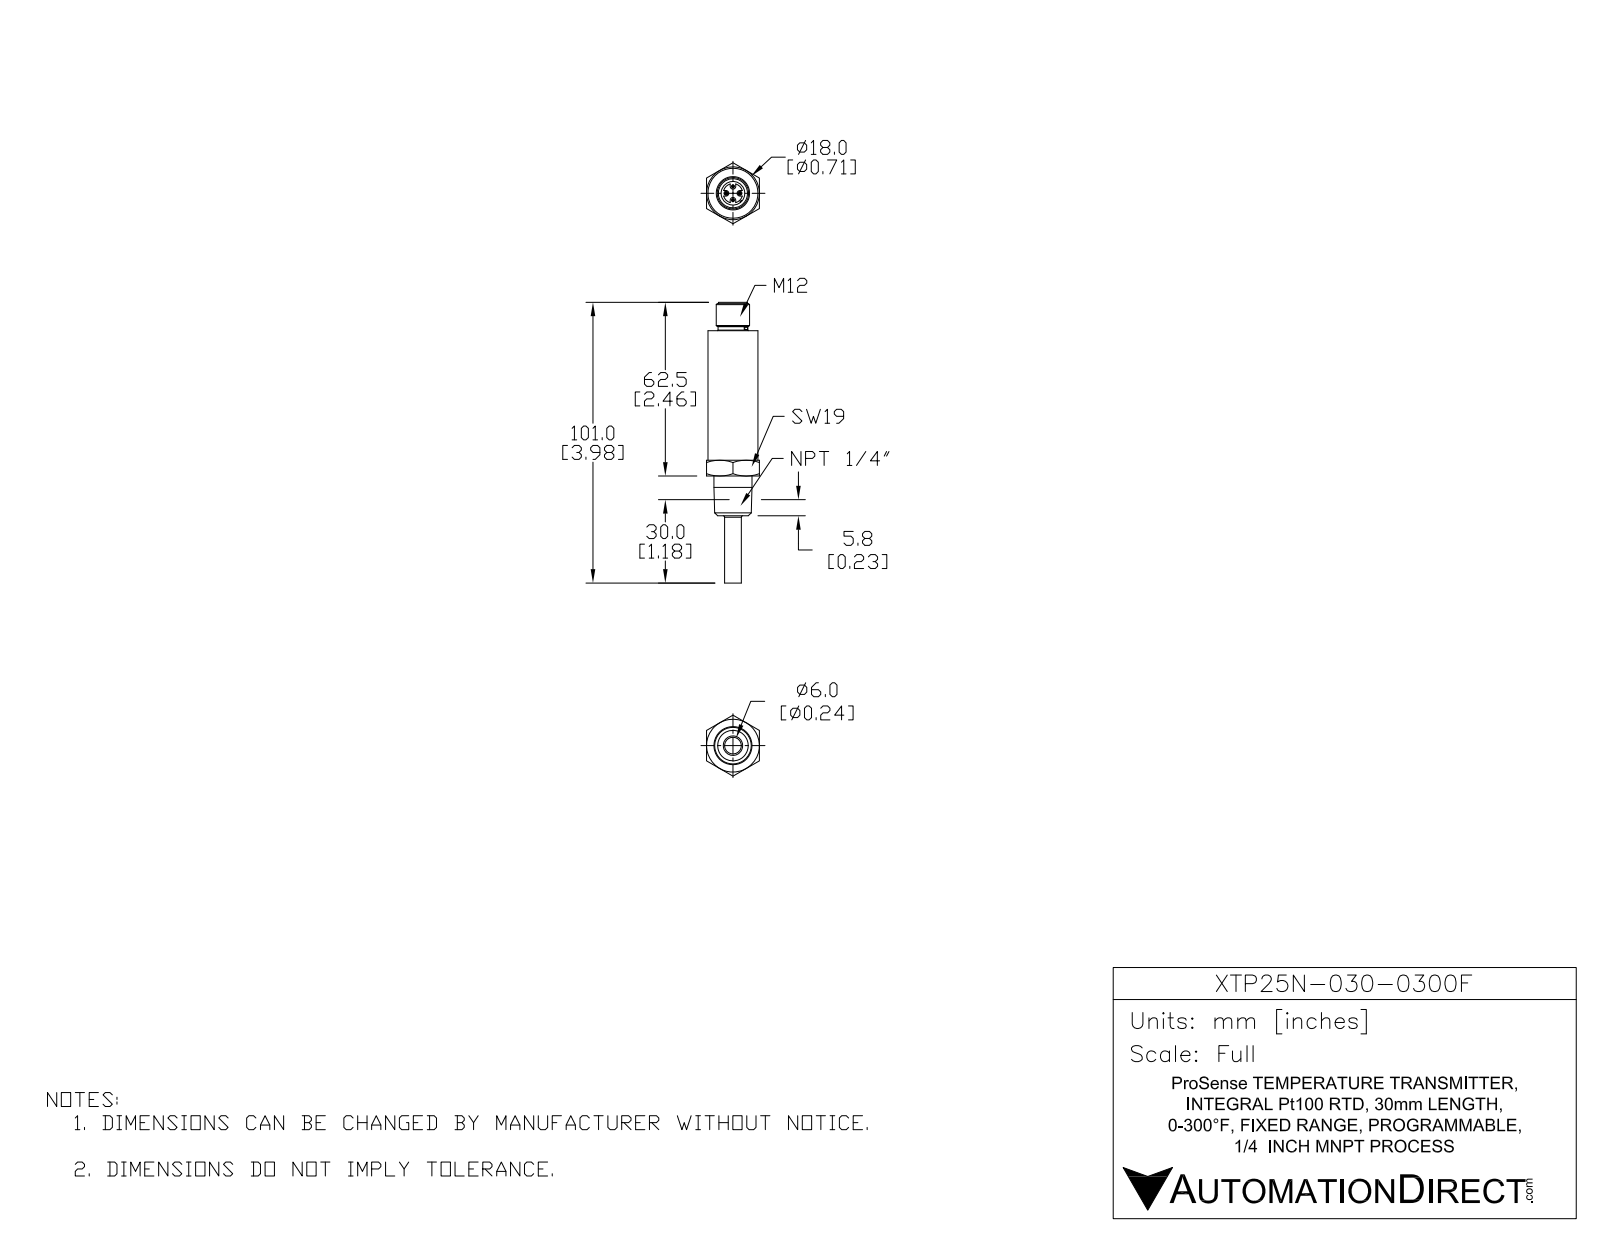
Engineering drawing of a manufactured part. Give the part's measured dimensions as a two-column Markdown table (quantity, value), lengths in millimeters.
| quantity | value |
| --- | --- |
| part name | XTP25N-030-0300F |
| STEP written by | SolidWorks 2015 (AUTOMOTIVE_DESIGN) |
| units | millimeters |
| bodies | 1 solid, 117 faces (43 planar, 34 cylindrical, 40 other) |
| overall size | 101 × 21.94 × 19 |
| volume | 16 667 mm³ |
| surface area | 5 627 mm² |
| round holes (diameter × count) | 4 × 1, 8.5 × 1 |
| round bosses / shafts (diameter × count) | 1.02 × 4, 18 × 1, 13.72 × 1, 12 × 1, 10.7 × 1, 10.5 × 1, 6 × 1 |
| partial cylindrical surfaces (radius × count) | 1 × 4, 3.5 × 1, 4.25 × 1 |
| main face-to-face distances | 19, 52.3, 14.3, 66.6, 20, 5.7, 46.6, 76.8, 62.5, 56.8 |
